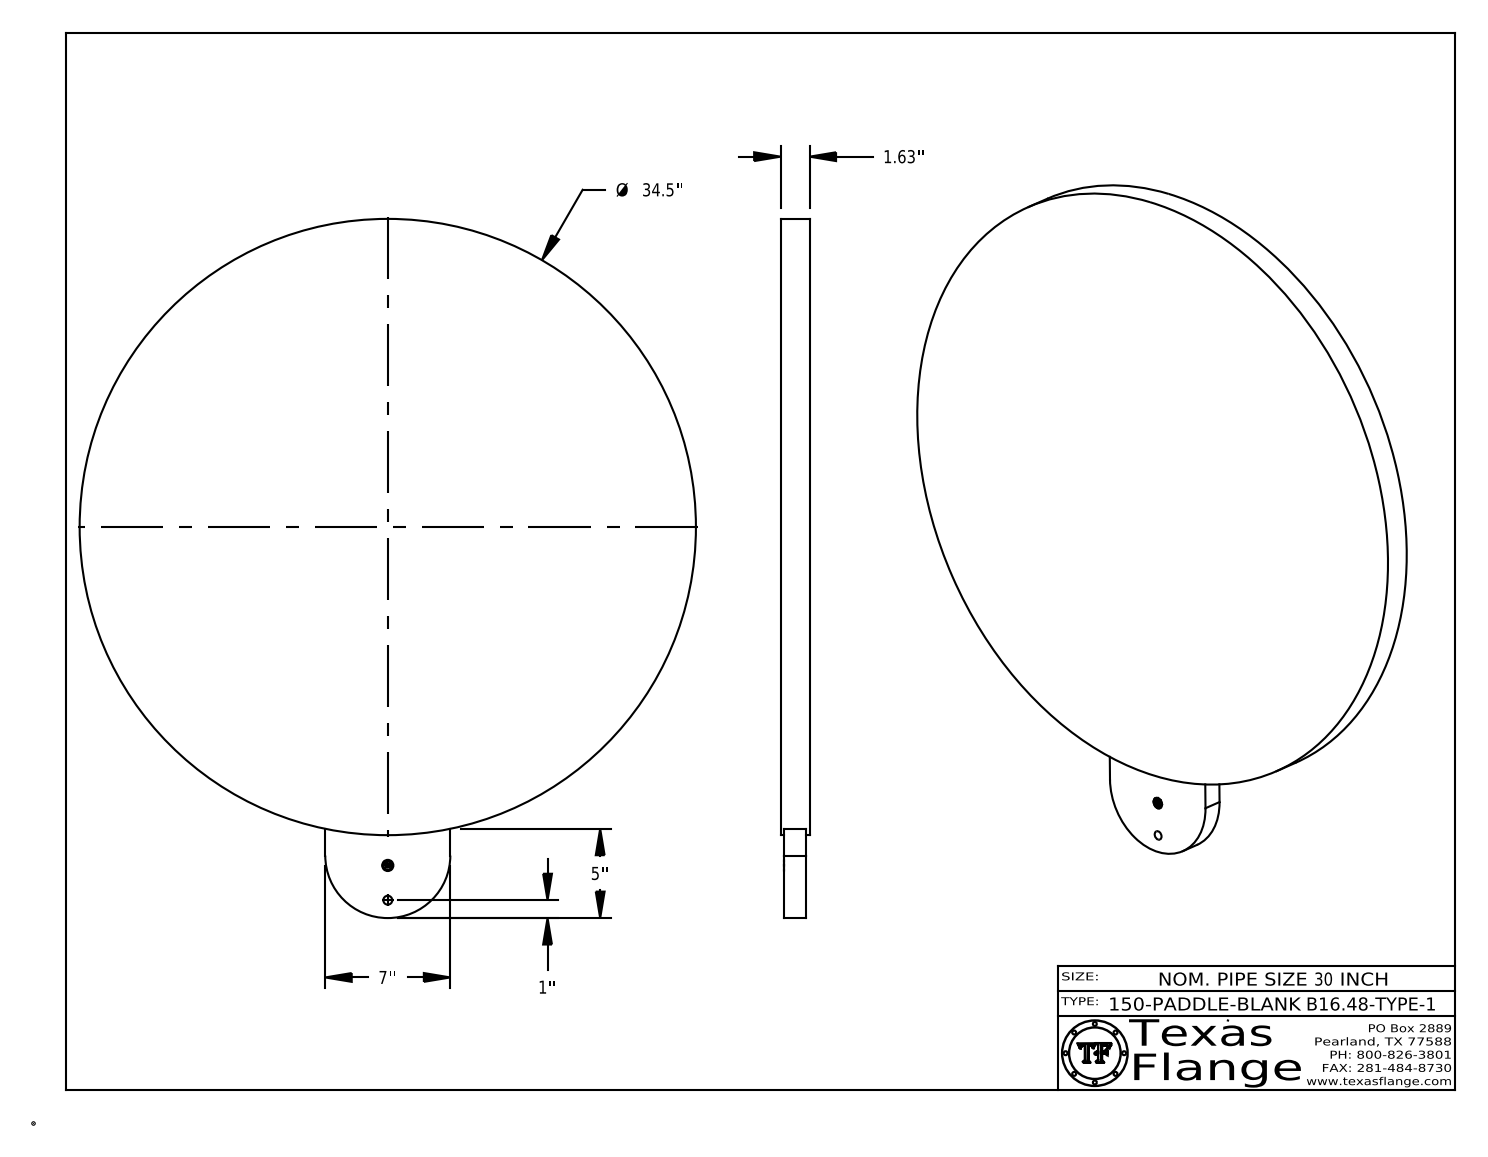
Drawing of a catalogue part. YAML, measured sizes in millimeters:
part_name: "30-150-PADDLE-BLANK-B16.48-TYPE-1"
step_written_by: "CATIA V5 STEP AP214 (AUTOMOTIVE_DESIGN)"
units: millimeters
bodies: {solids: 1, faces: 396, planar: 371, cylindrical: 25, other: 0}
overall_size: [994.2, 876.3, 41.3]
volume: 25450000
surface_area: 1363000
round_holes:
  - {diameter: 12.7, count: 1}
  - {diameter: 15.9, count: 1}
round_bosses_or_shafts:
  - {diameter: 1, count: 8}
  - {diameter: 876.3, count: 1}
  - {diameter: 12.5, count: 1}
partial_cylinders:
  - {radius: 88.9, count: 1}
face_to_face_distances: [41.3, 5.2, 36.1, 31, 177.8, 35.7, 30.6, 0.4, 5.5, 87.3]
hole_center_spacings: [49.4]
